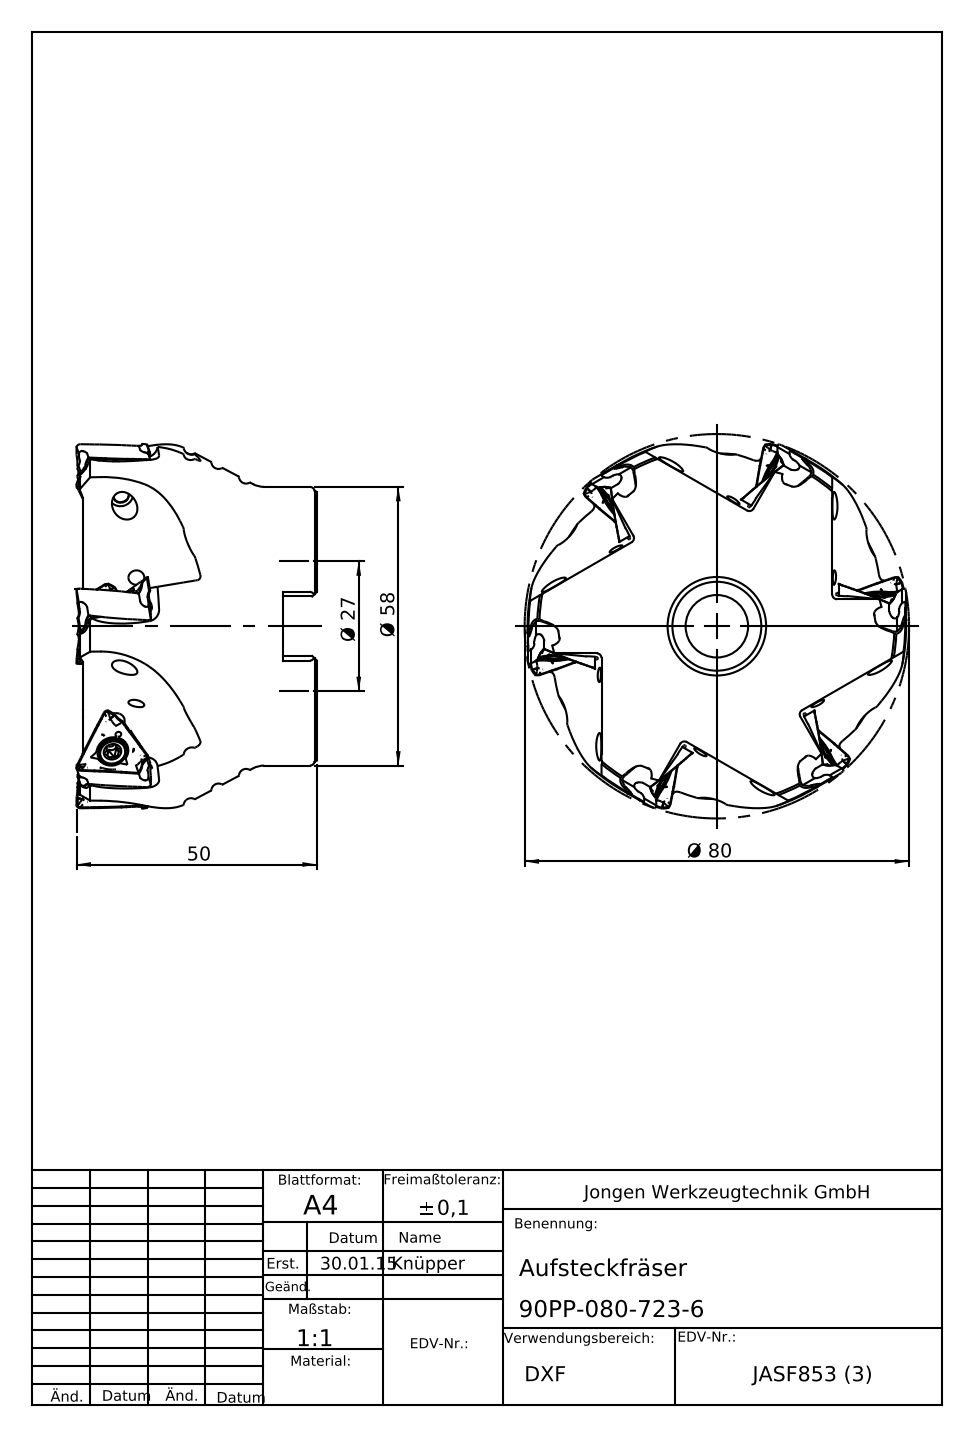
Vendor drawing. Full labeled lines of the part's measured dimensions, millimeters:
Part name (STEP PRODUCT): 90PP_080_723_6
STEP written by: SolidWorks 2016 (AUTOMOTIVE_DESIGN)
Units: millimetres
Bodies: 1 solid, 459 faces (128 planar, 167 cylindrical, 164 other)
Overall size (bounding box): 79.98 × 79.98 × 50.04
Volume: 155 810 mm³ · Surface area: 28 556 mm²
Round holes (diameter × count): ⌀3 ×6, ⌀13 ×1, ⌀18.5 ×1, ⌀27 ×1, ⌀27.15 ×1, ⌀27.3 ×1
Round bosses / shafts (diameter × count): ⌀58 ×1
Partial cylindrical surfaces — rounded edges, fillets, slot ends (radius × count): R1.25 ×48, R2 ×12, R2.5 ×12, R0.4 ×6, R1 ×6, R20 ×6
Main face-to-face distances: 48.7, 6.95, 41.75, 25, 18.05, 23.7, 12.4, 48, 34.7, 27.75
